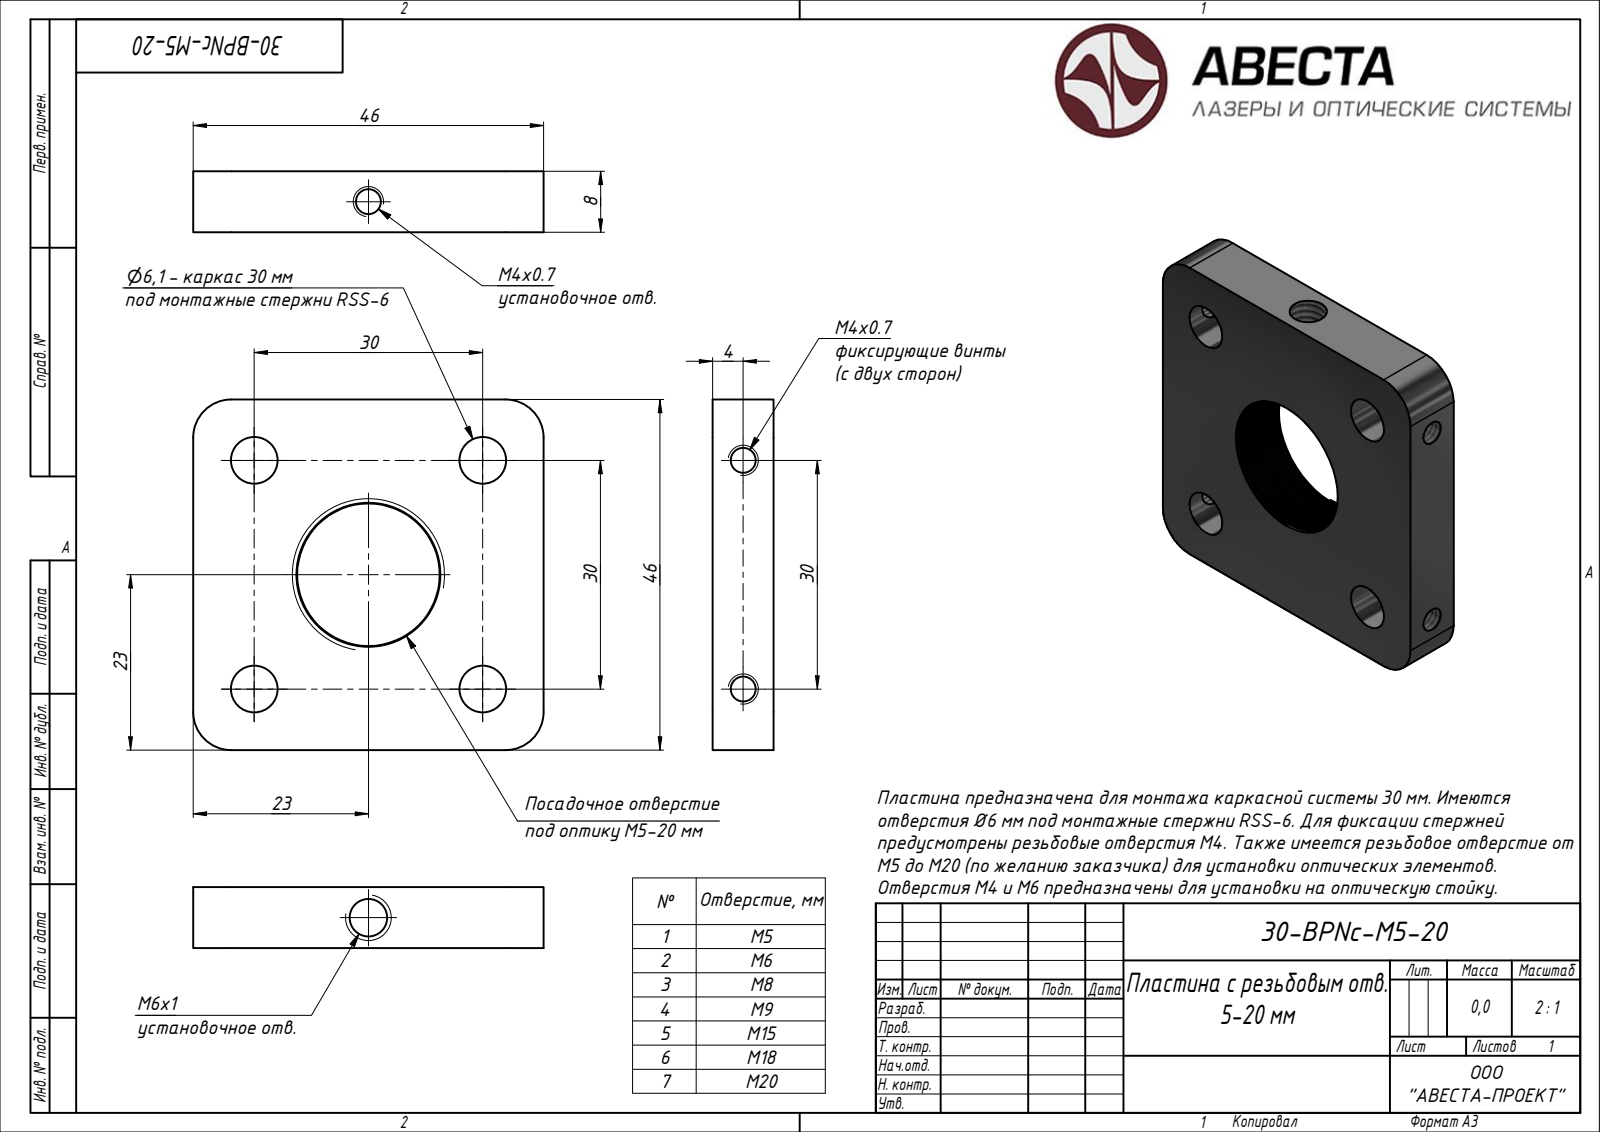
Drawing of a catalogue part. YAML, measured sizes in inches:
part_name: "30-BPNc-M20"
step_written_by: "Autodesk Inventor 2020 (AUTOMOTIVE_DESIGN)"
units: inches
bodies: {solids: 1, faces: 44, planar: 8, cylindrical: 32, other: 4}
overall_size: [1.811, 1.811, 0.323]
volume: 0.808
surface_area: 9.762
round_holes:
  - {diameter: 0.24, count: 4}
  - {diameter: 0.128, count: 3}
  - {diameter: 0.194, count: 1}
  - {diameter: 0.745, count: 1}
partial_cylinders:
  - {radius: 0.197, count: 4}
face_to_face_distances: [0.315, 1.811, 0.906]
hole_center_spacings: [1.181, 0.835, 1.67]
